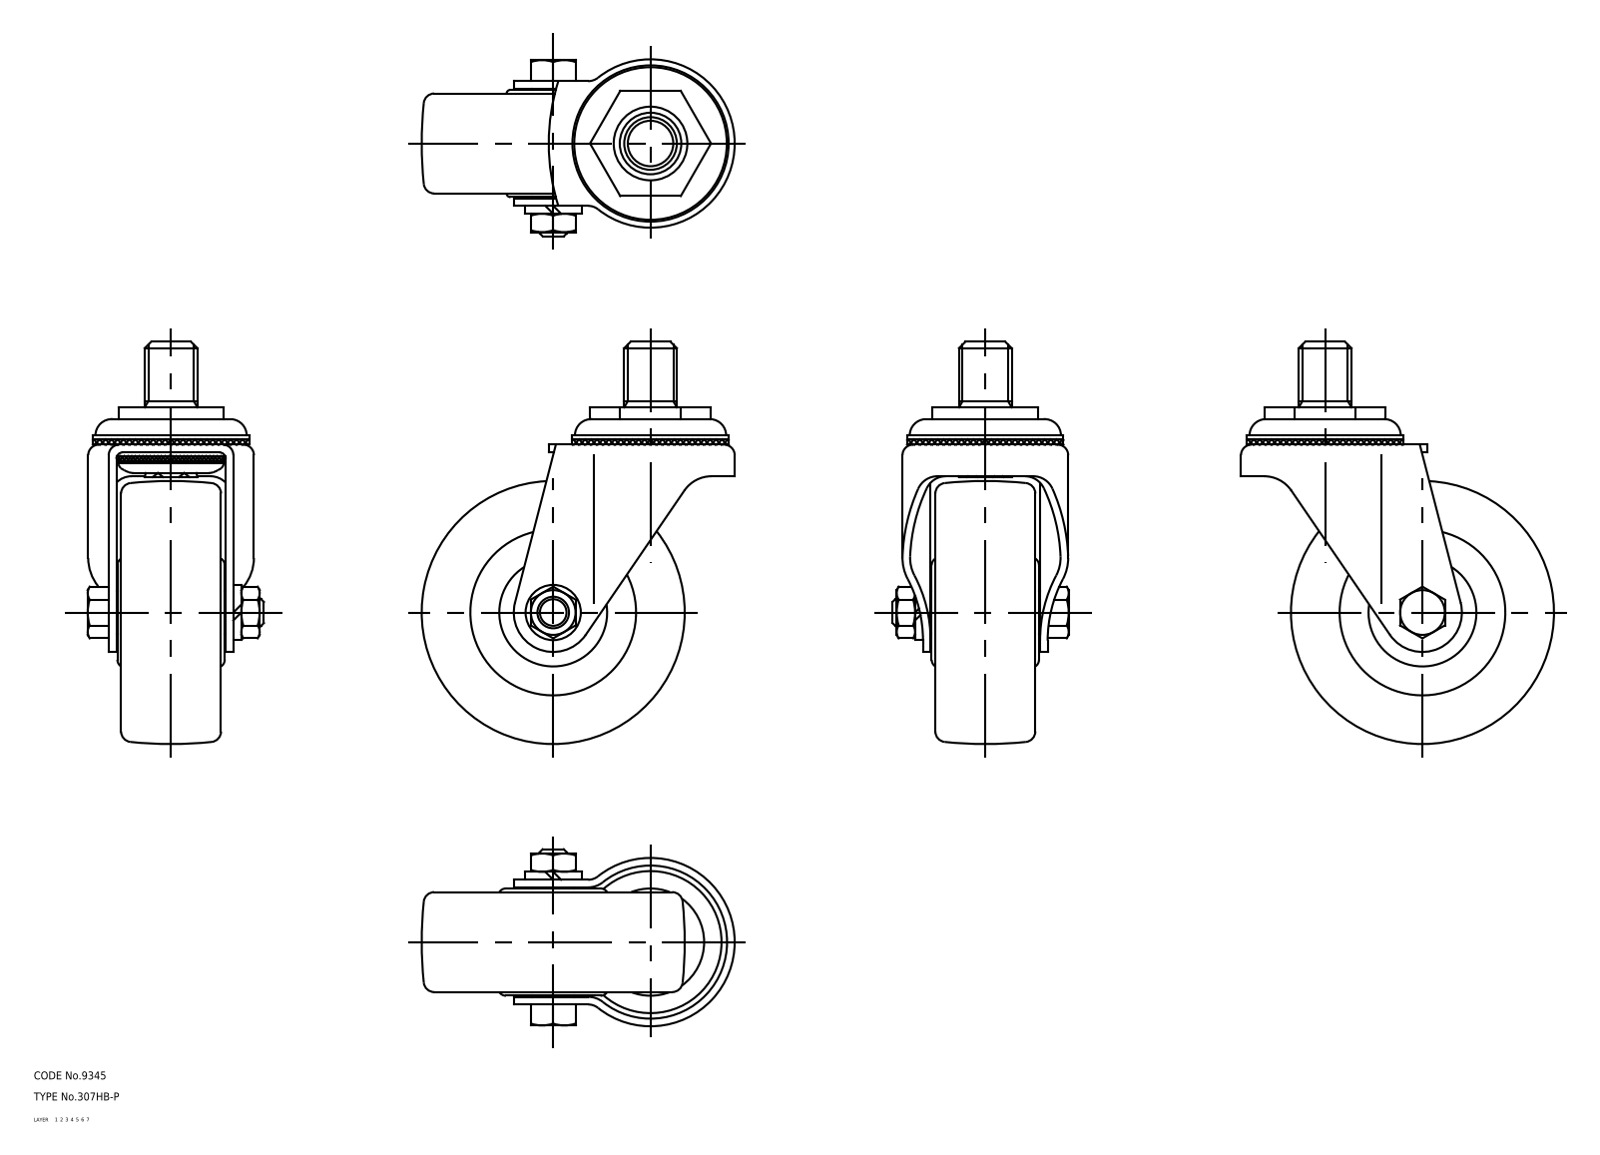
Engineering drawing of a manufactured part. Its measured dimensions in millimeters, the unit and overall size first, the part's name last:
Units: millimetres
Overall size (bounding box): 153 × 119 × 67
Volume: 344 727 mm³ · Surface area: 68 975 mm²
Bodies: 4 solids, 214 faces (0 planar, 0 cylindrical, 214 other)
Part name (STEP PRODUCT): 67123657; 67123670; 67123683; 67123696
STEP written by: CADfix (AUTOMOTIVE_DESIGN)
